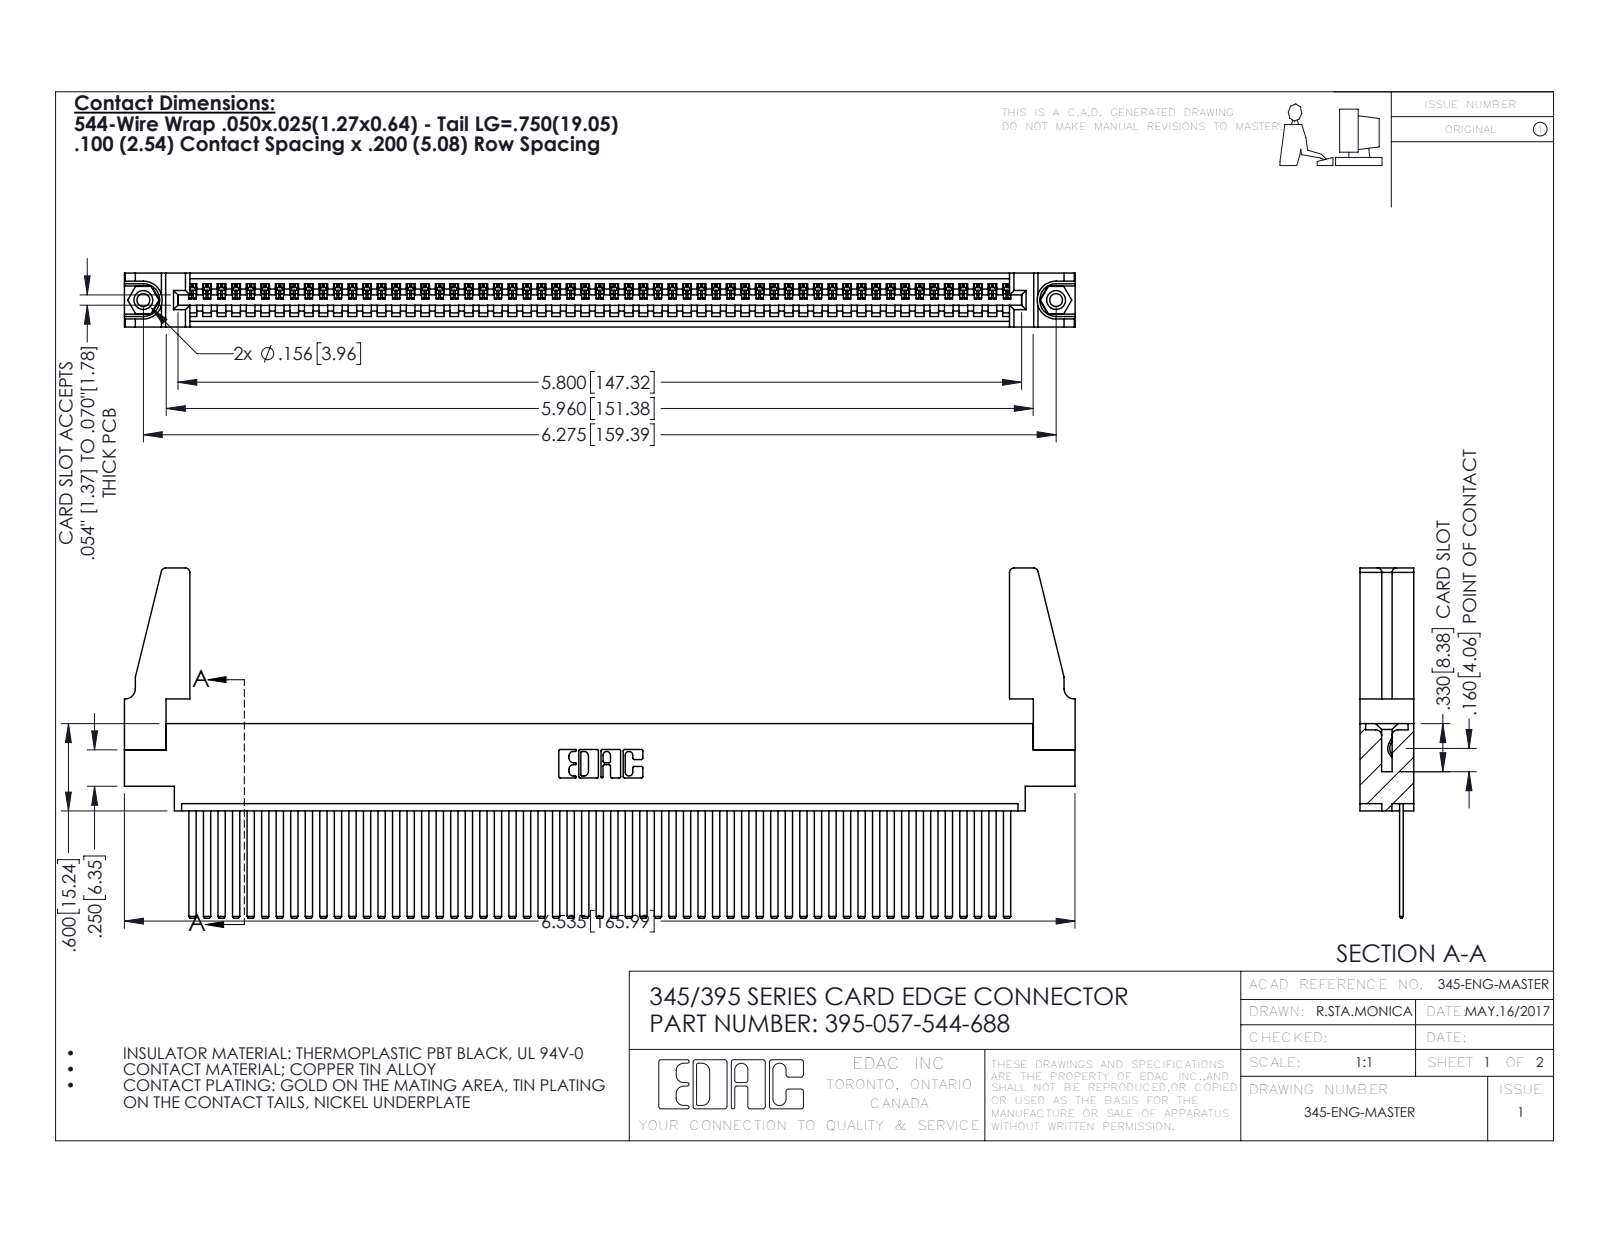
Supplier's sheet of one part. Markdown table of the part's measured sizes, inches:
| quantity | value |
| --- | --- |
| part name | 345 Part_0.170 Offset - 0.156 Dia-TH; 395-057-544-688; 345-220-078_345-220-088; 345-250-001_345-250-001-102 (+1 more) |
| STEP written by | SolidWorks 2016 (CONFIG_CONTROL_DESIGN) |
| units | inches |
| bodies | 62 solids, 3218 faces (2208 planar, 994 cylindrical, 16 other) |
| overall size | 6.536 × 2.407 × 0.37 |
| volume | 1.202 in³ |
| surface area | 42.29 in² |
| round holes (diameter × count) | 0.089 × 2, 0.125 × 2, 0.156 × 2, 0.064 × 1 |
| round bosses / shafts (diameter × count) | 0.155 × 2 |
| partial cylindrical surfaces (radius × count) | 0.006 × 114, 0.01 × 22, 0.03 × 8, 0.007 × 6, 0.031 × 6, 0.026 × 3, 0.031 × 2, 0.04 × 2 |
| main face-to-face distances | 0.072, 0.298, 0.098, 0.272, 0.025, 0.37, 0.2, 0.225, 0.175, 0.149 |
| hole center spacings | 0.27, 6.039, 6.275 |
